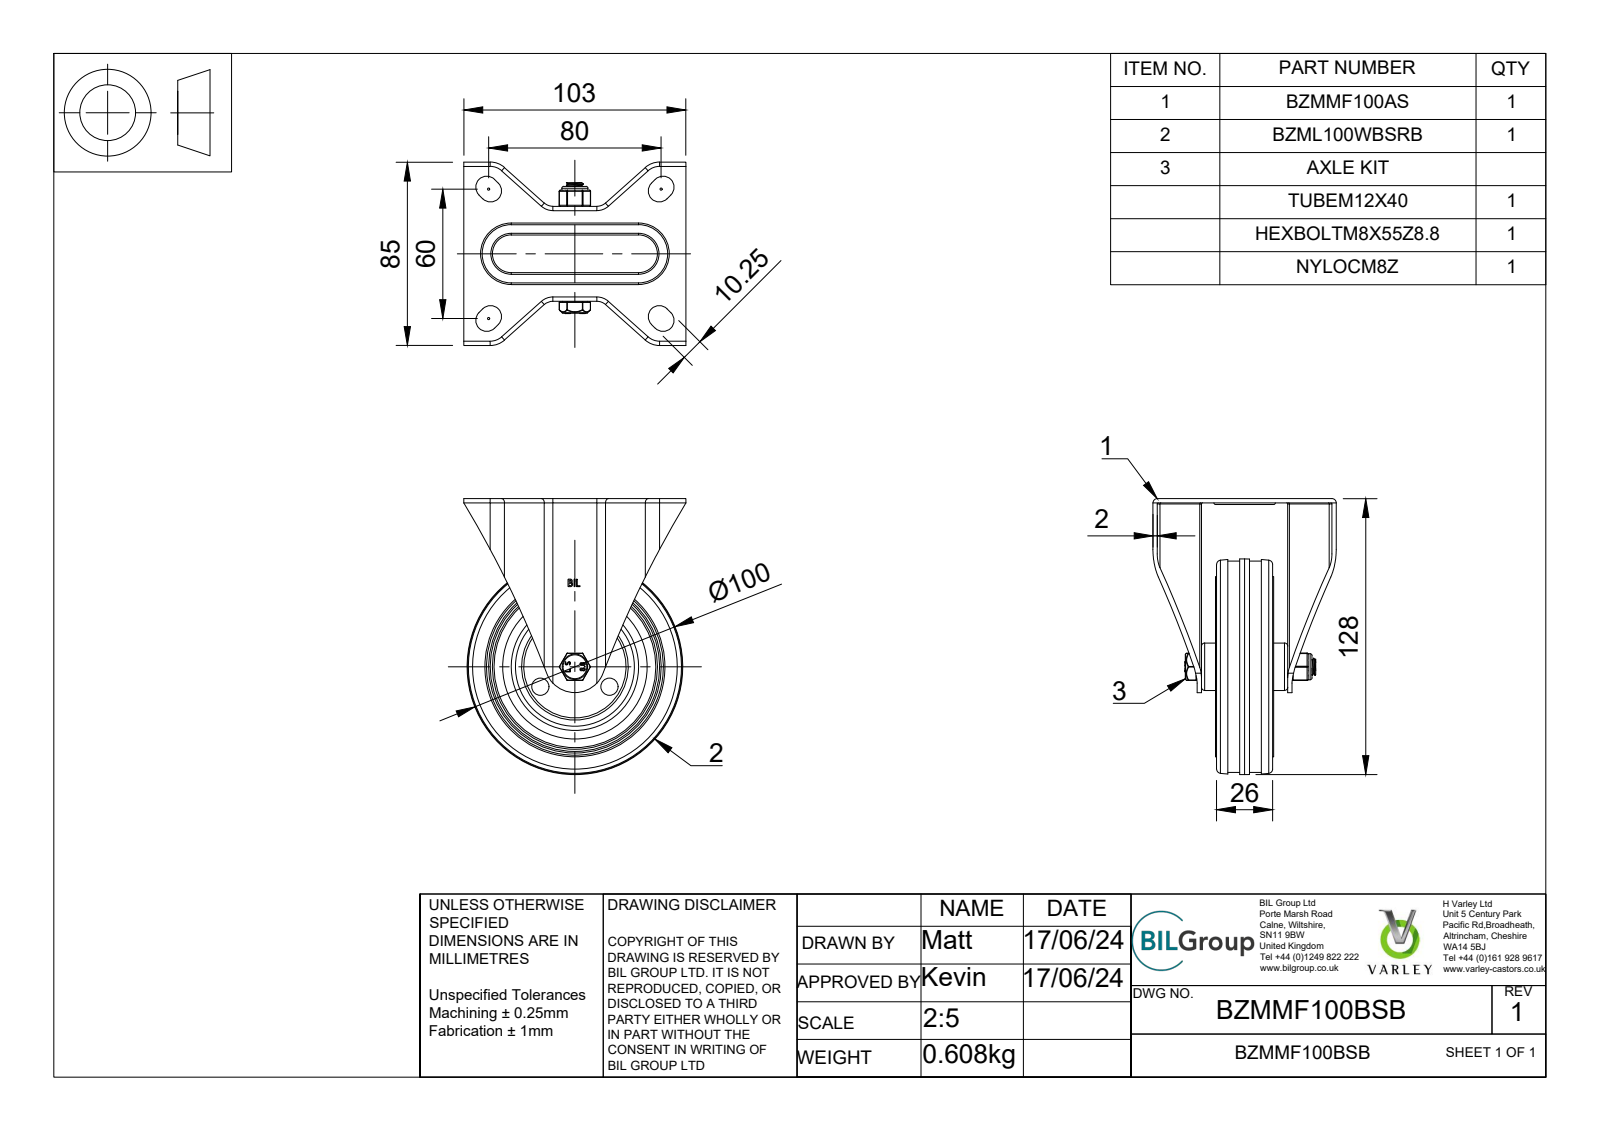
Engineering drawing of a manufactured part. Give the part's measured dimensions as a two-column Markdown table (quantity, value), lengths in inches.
| quantity | value |
| --- | --- |
| part name | BZMMF100BSB v3; BZMMF100AS v1; BZMMF100AS; ZINC PLATED, PRESSED STEEL BRACKET (+7 more) |
| STEP written by | Autodesk Translation Framework v13.14.0.145 (AUTOMOTIVE_DESIGN) |
| units | inches |
| bodies | 19 solids, 562 faces (225 planar, 220 cylindrical, 117 other) |
| overall size | 5.039 × 4.055 × 3.346 |
| volume | 12.11 in³ |
| surface area | 151.3 in² |
| round holes (diameter × count) | 0.197 × 3, 0.026 × 2, 0.315 × 1, 0.325 × 1, 0.331 × 1, 0.339 × 1, 0.48 × 1, 0.492 × 1, 0.787 × 1, 2.005 × 1, 2.638 × 1, 2.953 × 1 |
| round bosses / shafts (diameter × count) | 0.138 × 8, 0.315 × 3, 3.937 × 1, 3.858 × 1, 3.287 × 1, 3.15 × 1, 3.012 × 1, 0.866 × 1 |
| partial cylindrical surfaces (radius × count) | 0.02 × 26, 0.01 × 12, 0.03 × 8, 0.079 × 8, 0.202 × 8, 0.013 × 4, 0.025 × 4, 0.118 × 4 |
| main face-to-face distances | 0.079, 0.02, 1.024, 0.561, 0.827, 1.299, 0.276, 0.354, 1.378, 1.654 |
| hole center spacings | 0.728, 1.261, 0.127, 0.098, 0.603, 0.659, 0.689, 0.786 |
